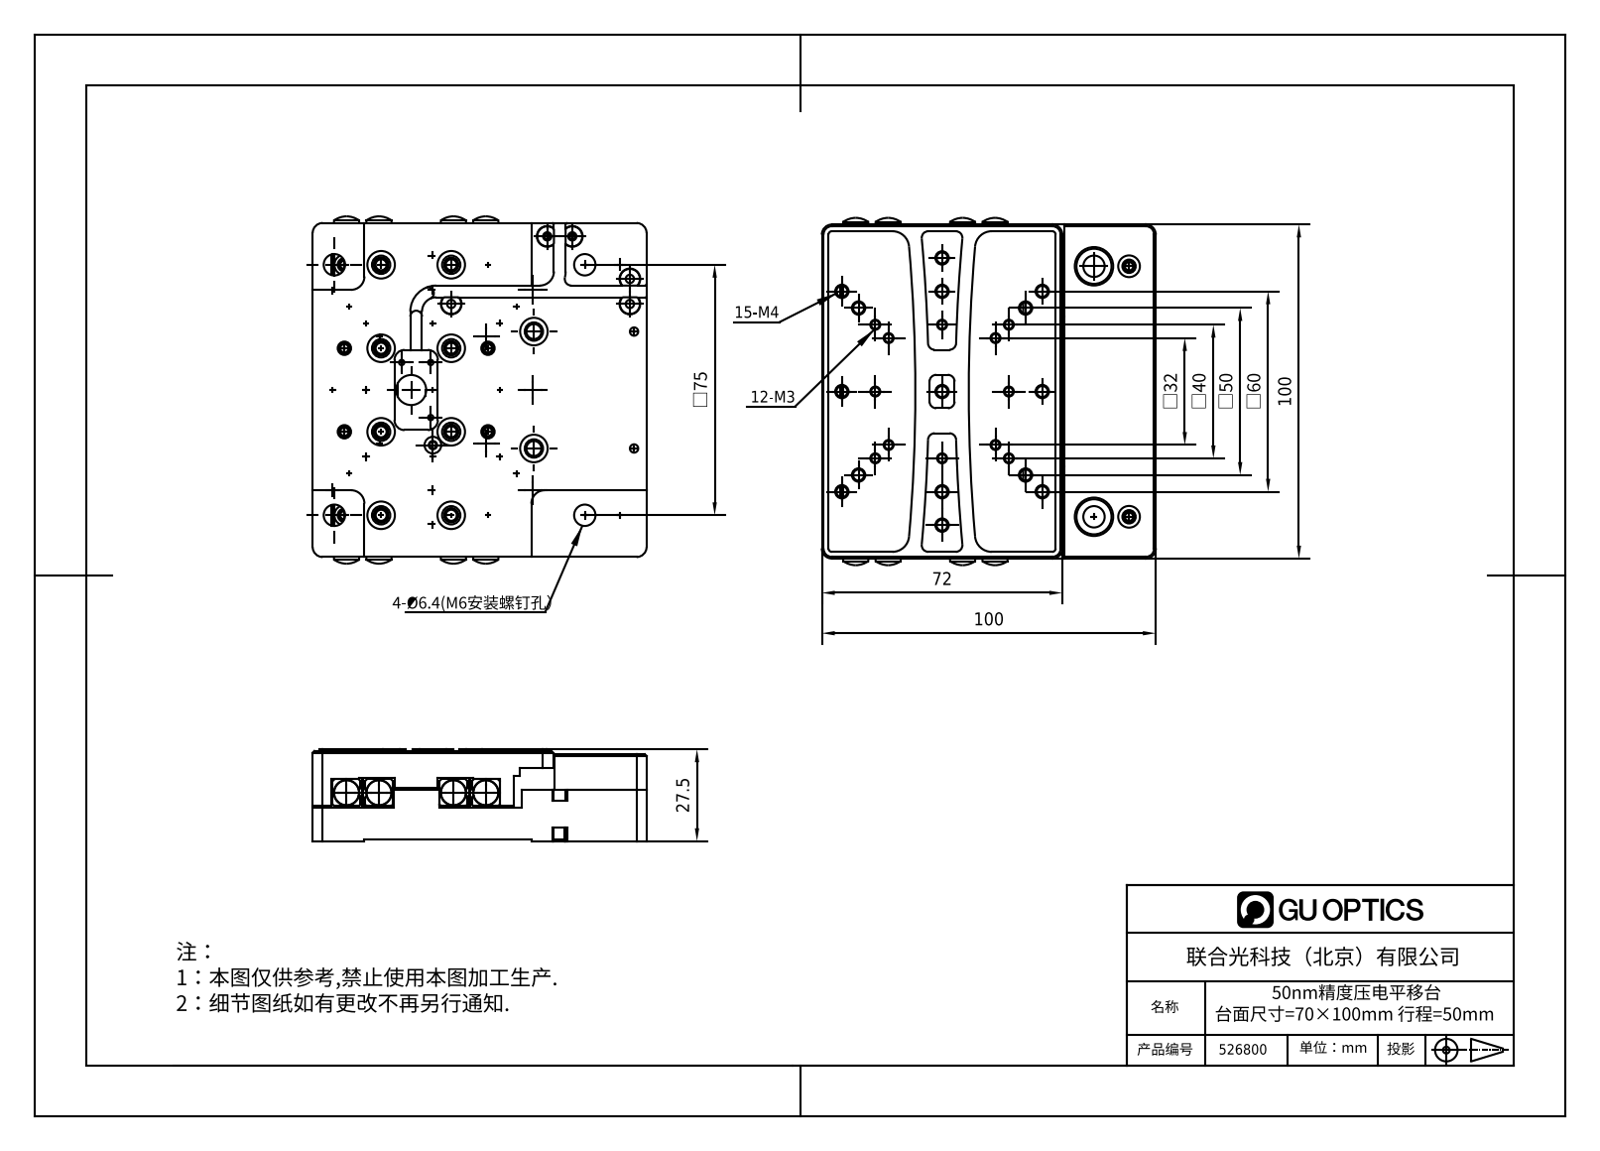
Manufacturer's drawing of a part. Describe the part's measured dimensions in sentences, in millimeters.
The part is named "GU-LS3T系列平移台 70台面". Its 3-D file was written by "SolidWorks 2016 (AUTOMOTIVE_DESIGN)". It is 0 solids with 1292 faces: 580 planar, 415 cylindrical and 297 other. Overall it measures 105 by 100 by 27.5 millimeters. Round holes: 21 of diameter 3, 21 of diameter 3.3, 21 of diameter 4, 20 of diameter 2.5, 12 of diameter 7.5, 8 of diameter 5.4, 6 of diameter 4.3, 6 of diameter 8.2, 4 of diameter 1.57, 4 of diameter 3.24, 4 of diameter 4.5, 4 of diameter 6.4. Round bosses or shafts: 12 of diameter 4, 10 of diameter 7, 4 of diameter 7.53, 2 of diameter 3.24. Partial cylindrical surfaces (rounded edges, fillets, slot ends): 17 of radius 1, 13 of radius 2, 12 of radius 3, 5 of radius 1.5, 4 of radius 2.6, 4 of radius 5, 3 of radius 7.9, 3 of radius 12.1. The main face-to-face distances are 0.5, 6.5, 16, 7, 7.5, 20, 4.5, 20.5, 22.5, 3. The hole center spacings are 25, 50, 75, 37.84, 12.53, 16.06, 17.37, 20.66.
